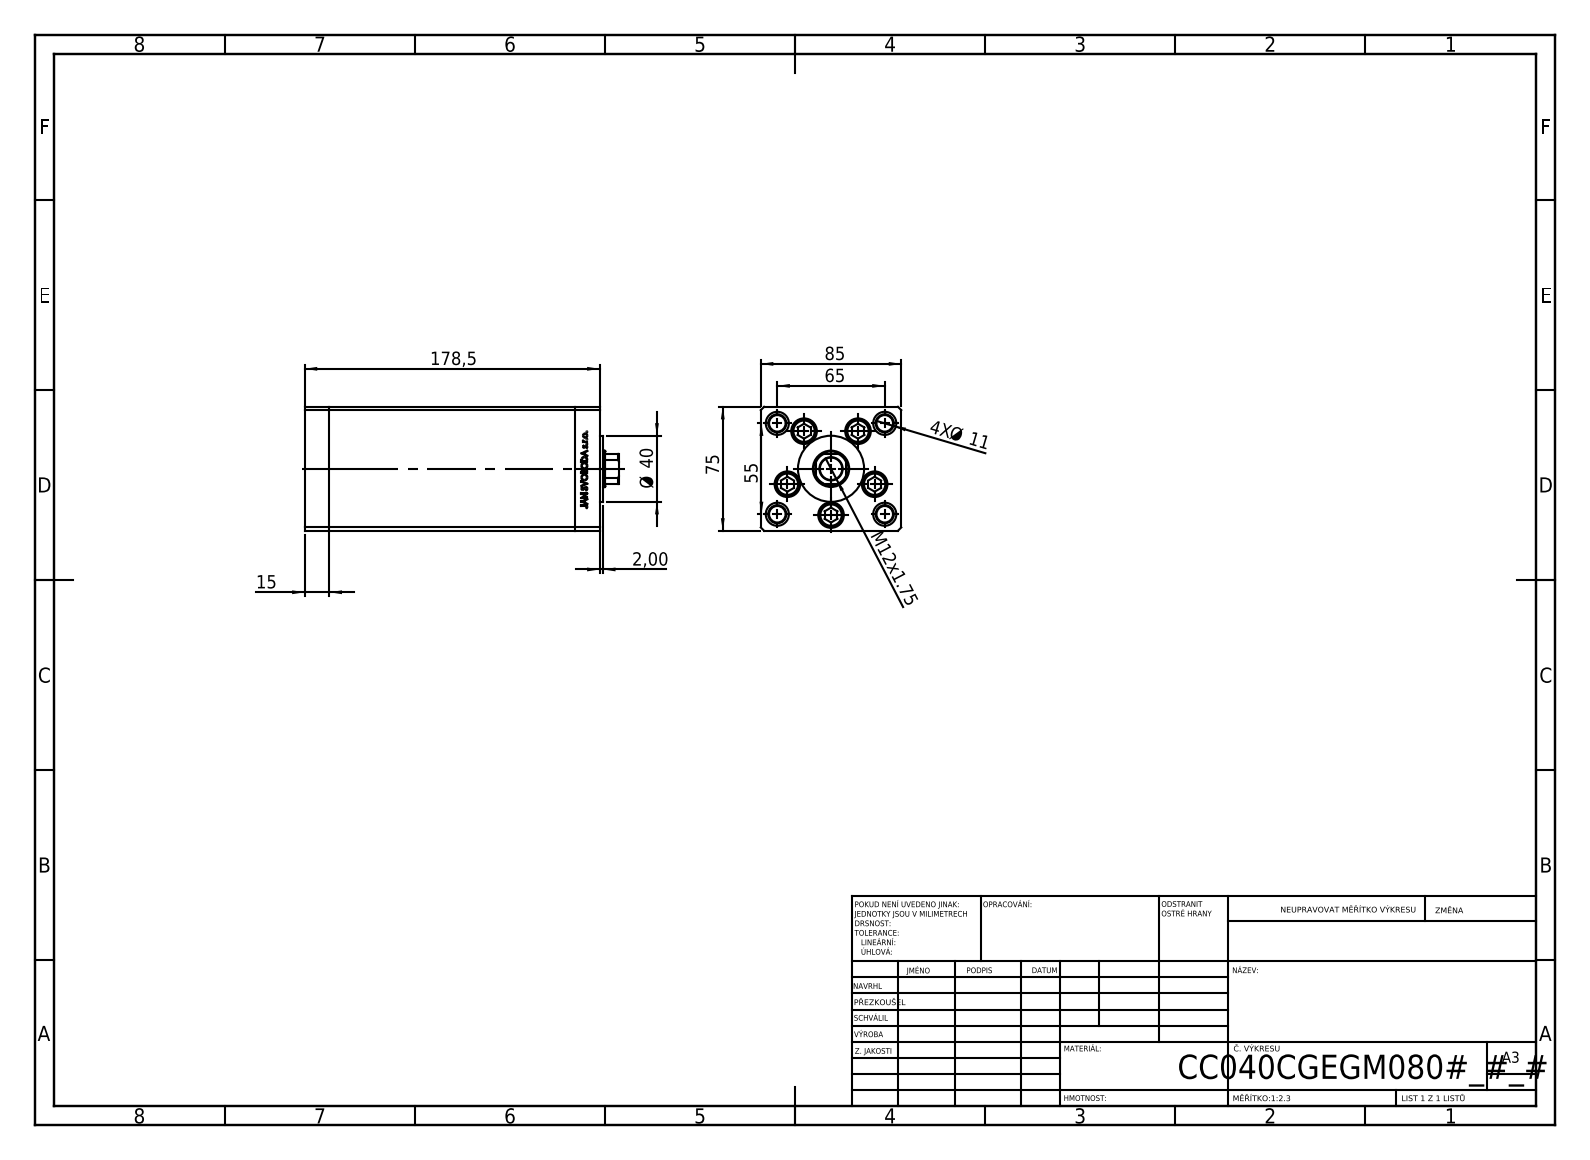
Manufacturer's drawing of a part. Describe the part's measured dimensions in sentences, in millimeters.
The part is named "V220C FRONT; ALLEN BOLT; V220C_C MIDDLE; V220C BACK_C (+1 more)". Its 3-D file was written by "SolidWorks 2019 (CONFIG_CONTROL_DESIGN)". It is 13 solids with 1159 faces: 538 planar, 159 cylindrical and 462 other. Overall it measures 190 by 85 by 75 millimeters. Its volume is 949 001 cubic millimeters and its surface area 179 253 square millimeters. Round holes: 9 of diameter 11, 5 of diameter 15.5, 4 of diameter 10, 4 of diameter 14, 1 of diameter 13.5, 1 of diameter 14.5, 1 of diameter 22. Round bosses or shafts: 5 of diameter 8, 4 of diameter 14.5, 1 of diameter 40. Partial cylindrical surfaces (rounded edges, fillets, slot ends): 2 of radius 0.93, 1 of radius 10.5. The main face-to-face distances are 85, 75, 15, 148.5, 163.5, 10.5, 178.5, 34.25, 144.25, 129.25. The hole center spacings are 28, 42.57, 16.86, 19.17, 32.33, 32.5, 33.63, 37.33.
